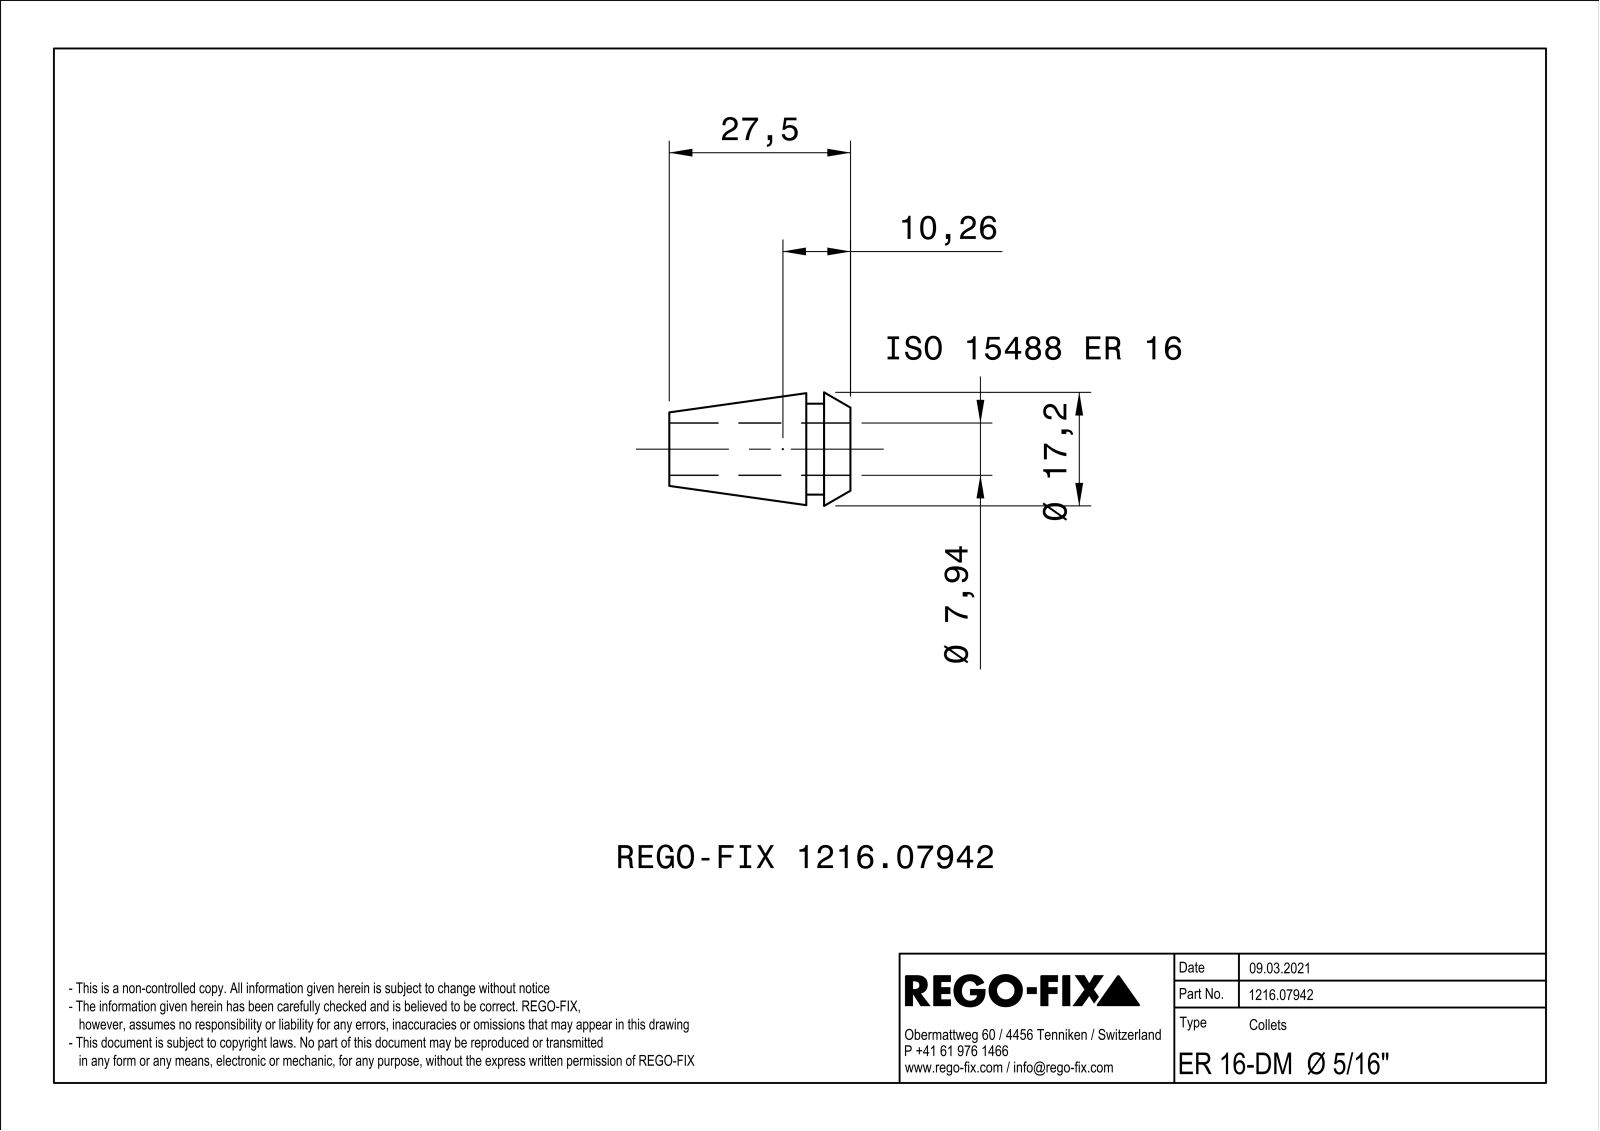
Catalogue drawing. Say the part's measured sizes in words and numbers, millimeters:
The part is named "NOCUT". Its 3-D file was written by "SIEMENS PLM Software Solid Edge ST10 (AUTOMOTIVE_DESIGN)". It is 1 solid with 154 faces: 80 planar, 9 cylindrical and 65 other. Overall it measures 27.5 by 16.99 by 16.99 millimeters. Its volume is 2 480 cubic millimeters and its surface area 3 668 square millimeters. Round holes: 1 of diameter 7.94. Round bosses or shafts: 1 of diameter 13.8. The main face-to-face distances are 0.6, 6.7, 4, 2.7, 27.5, 23.5, 20.8, 13, 9, 6.3.
